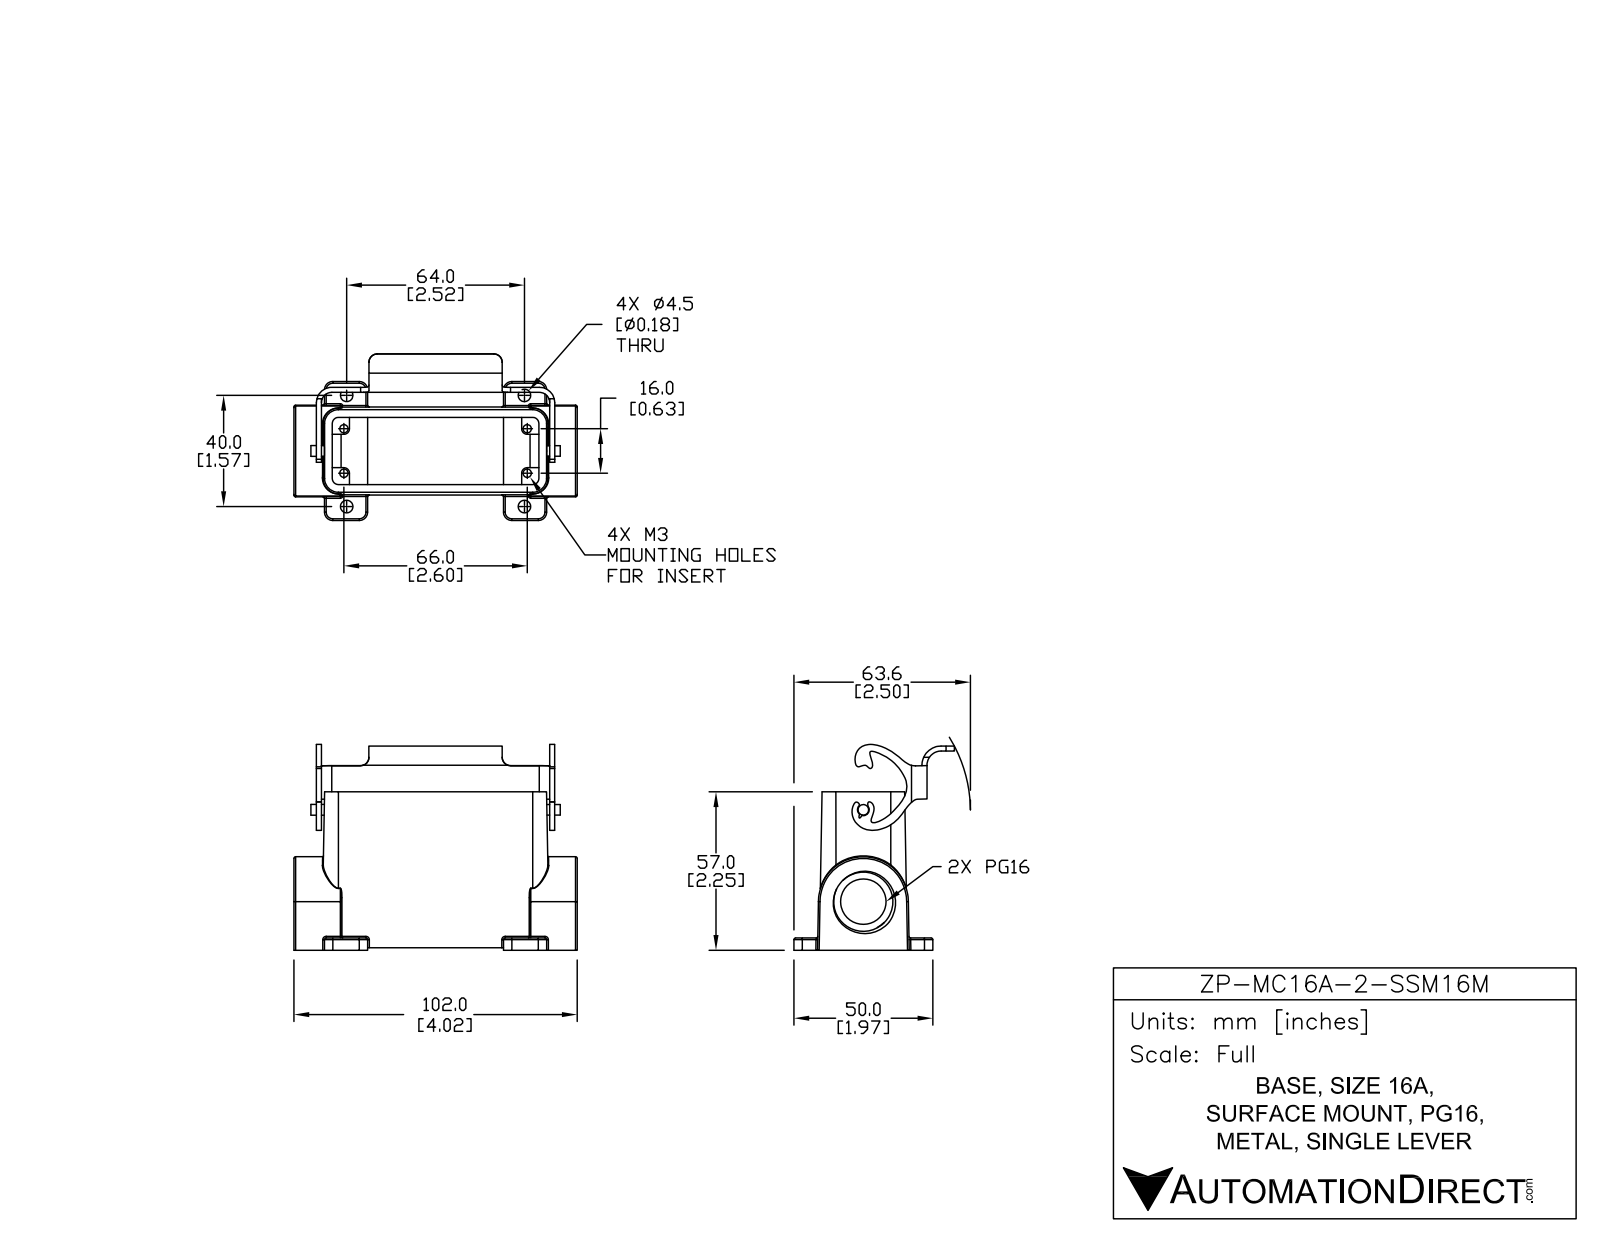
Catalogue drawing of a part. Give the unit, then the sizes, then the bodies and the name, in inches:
Units: inches
Overall size (bounding box): 4.016 × 2.913 × 2.359
Round holes (diameter × count): ⌀0.118 ×4, ⌀0.177 ×4, ⌀0.643 ×1, ⌀0.839 ×1
Round bosses / shafts (diameter × count): ⌀0.154 ×1, ⌀0.15 ×1
Partial cylindrical surfaces — rounded edges, fillets, slot ends (radius × count): R0.024 ×24, R0.118 ×12, R0.012 ×10, R0.079 ×4, R0.148 ×2, R0.219 ×2, R0.083 ×1, R0.201 ×1
Main face-to-face distances: 0.109, 0.109, 0.071, 0.036, 0.145, 0.026, 0.787, 3.228, 0.175, 0.139
Hole centre spacings: 0.474, 1.103, 2.602, 2.786, 0.63, 1.575, 2.52, 2.598
Volume: 3.902 in³ · Surface area: 62.45 in²
Bodies: 2 solids, 310 faces (89 planar, 147 cylindrical, 74 other)
Part name (STEP PRODUCT): ZP-MC16A-2-SSM16M
STEP written by: SolidWorks 2014 (AUTOMOTIVE_DESIGN)
